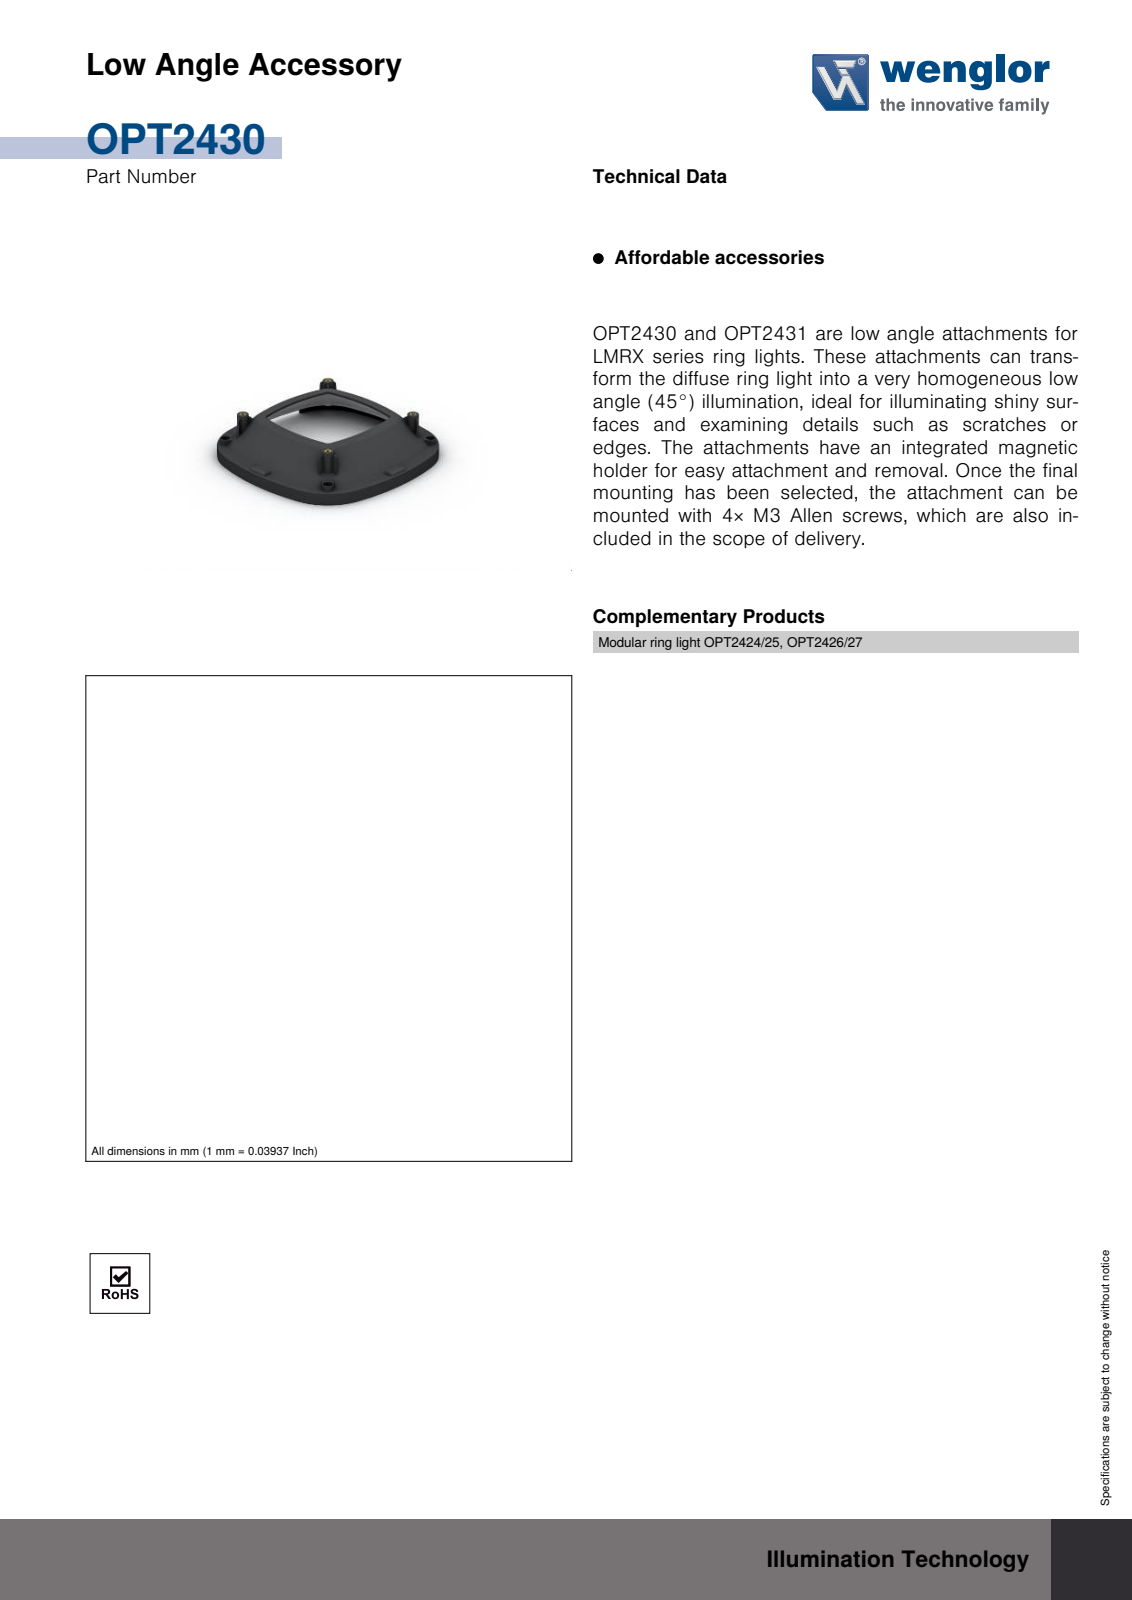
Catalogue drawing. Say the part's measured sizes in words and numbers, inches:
The part is named "OPT2430". Its 3-D file was written by "SolidWorks 2021 (AUTOMOTIVE_DESIGN)". It is 1 solid with 991 faces: 130 planar, 228 cylindrical and 633 other. Overall it measures 5.357 by 5.275 by 1.211 inches. Its volume is 1.9 cubic inches and its surface area 60.25 square inches. Round holes: 4 of diameter 0.118, 4 of diameter 0.126, 4 of diameter 0.167. Partial cylindrical surfaces (rounded edges, fillets, slot ends): 64 of radius 0.008, 56 of radius 0.01, 20 of radius 0.079, 14 of radius 0.012, 9 of radius 0.039, 8 of radius 0.02, 6 of radius 4.925, 4 of radius 0.118. The main face-to-face distances are 0.079, 0.789, 0.711, 0.868, 0.266, 0.344, 1.055, 1.134, 0.157, 0.632. The hole center spacings are 3.228, 3.588, 0.485, 3.588, 3.915, 4.566, 5.051, 3.229.
